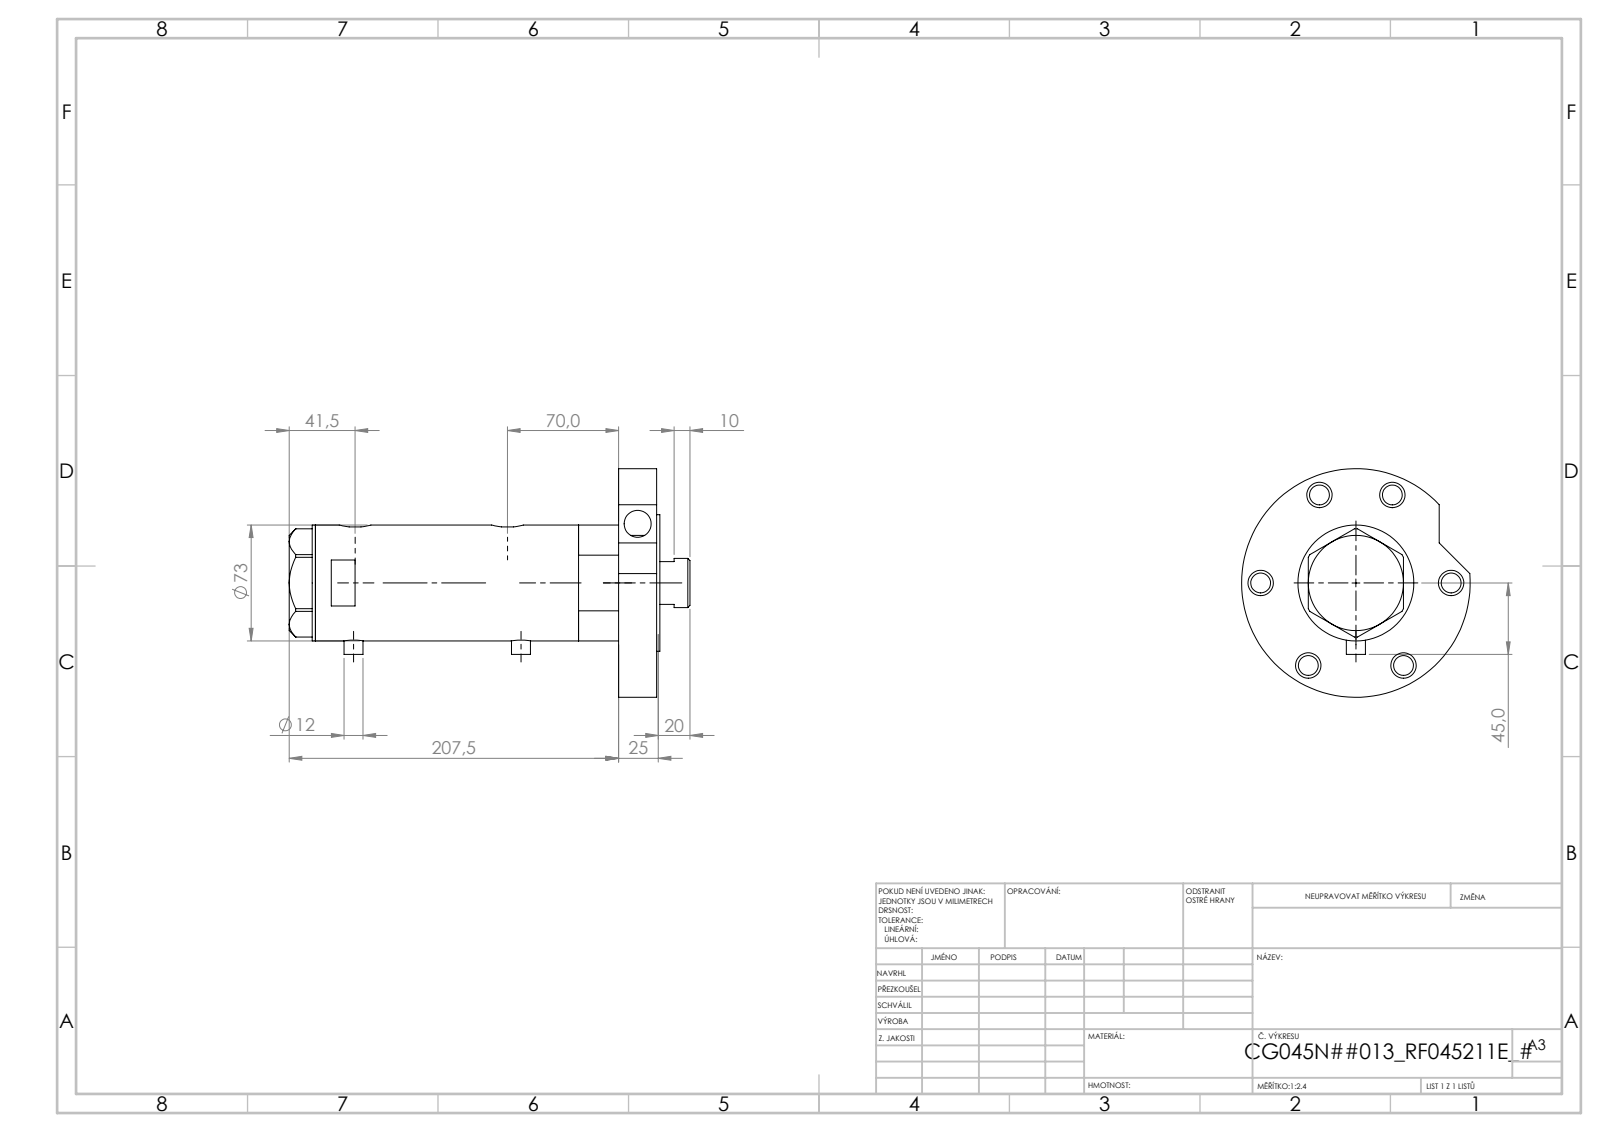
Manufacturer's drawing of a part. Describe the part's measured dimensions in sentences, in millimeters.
The part is named "V270CG_RF211E; V270CG_FRONT; V270CG_BACK; V270CG_VC (+1 more)". Its 3-D file was written by "SolidWorks 2019 (CONFIG_CONTROL_DESIGN)". It is 5 solids with 169 faces: 61 planar, 88 cylindrical and 20 other. Overall it measures 204.52 by 144 by 144 millimeters. Its volume is 984 782 cubic millimeters and its surface area 178 577 square millimeters. Round holes: 8 of diameter 12.5, 6 of diameter 16, 2 of diameter 5, 2 of diameter 13.16, 1 of diameter 10.5, 1 of diameter 17, 1 of diameter 32, 1 of diameter 33.5, 1 of diameter 45, 1 of diameter 48, 1 of diameter 60, 1 of diameter 64. Round bosses or shafts: 2 of diameter 12, 1 of diameter 144, 1 of diameter 86, 1 of diameter 73, 1 of diameter 58, 1 of diameter 31. Partial cylindrical surfaces (rounded edges, fillets, slot ends): 2 of radius 10. The main face-to-face distances are 24, 140.46, 26, 164.46, 2, 166.46, 80.16, 60.3, 84.3, 54.16. The hole center spacings are 60, 64.65, 66.67, 99.77, 103.92, 107.62, 119.74, 0.99.
